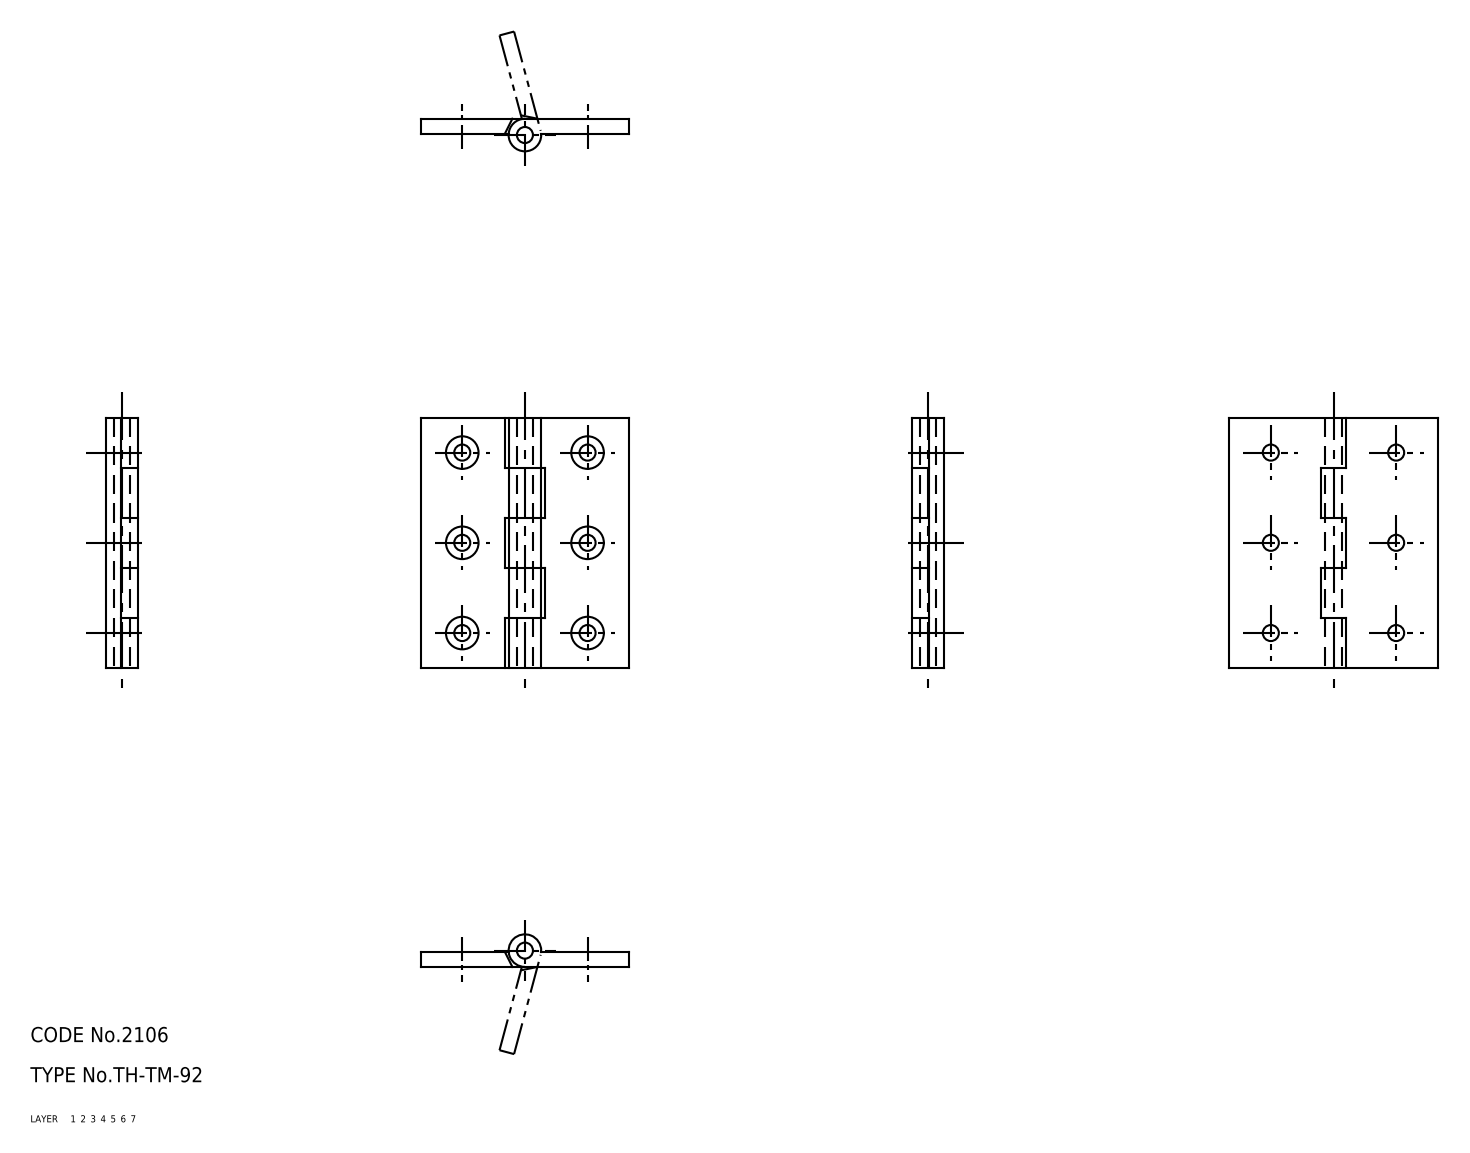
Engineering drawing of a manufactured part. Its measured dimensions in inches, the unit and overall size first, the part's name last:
Units: inches
Overall size (bounding box): 1.969 × 1.634 × 0.256
Volume: 0.413 in³ · Surface area: 10.02 in²
Bodies: 3 solids, 71 faces (0 planar, 0 cylindrical, 71 other)
Part name (STEP PRODUCT): 67113343; 67113356; 67113369
STEP written by: CADfix (AUTOMOTIVE_DESIGN)
